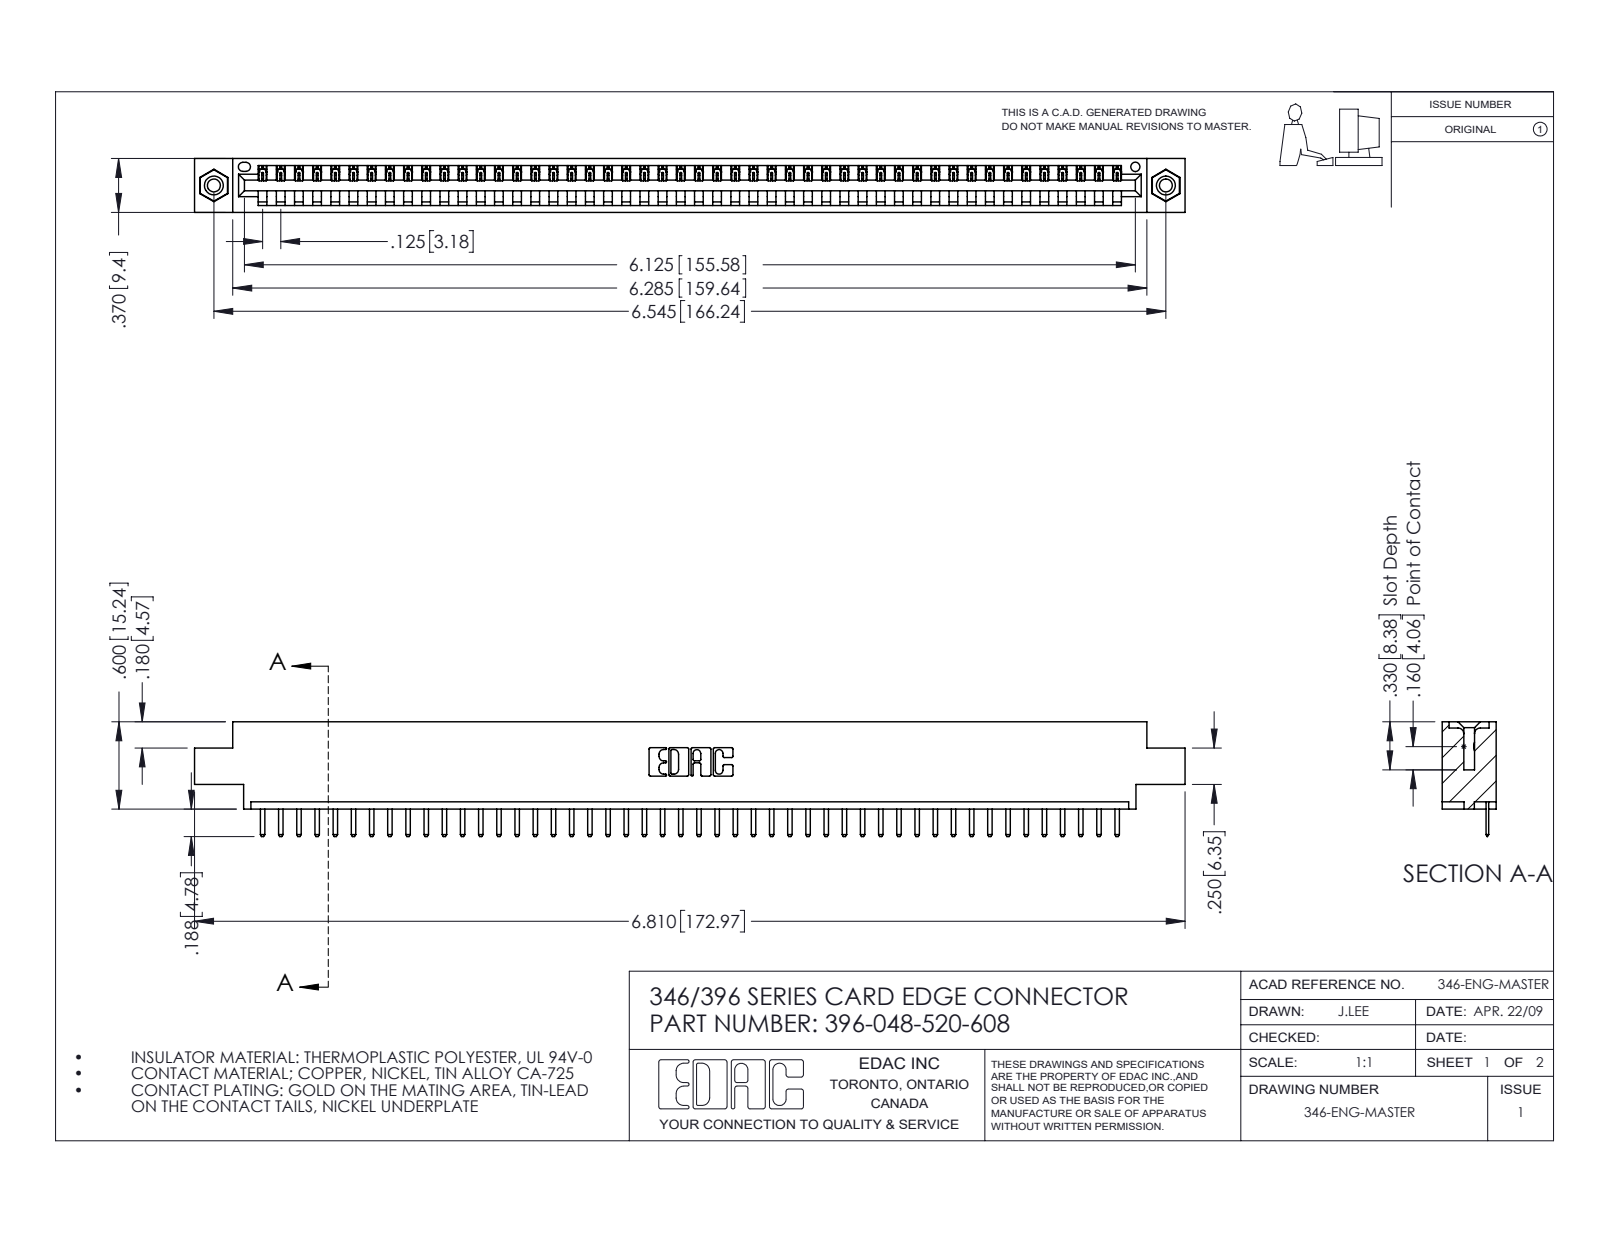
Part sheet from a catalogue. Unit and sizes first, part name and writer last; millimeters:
Units: millimetres
Overall size (bounding box): 173 × 20 × 9.4
Round holes (diameter × count): ⌀2.3 ×2, ⌀3.2 ×2, ⌀4 ×2, ⌀1.6 ×1
Round bosses / shafts (diameter × count): ⌀3.9 ×2
Partial cylindrical surfaces — rounded edges, fillets, slot ends (radius × count): R0.3 ×98, R0.2 ×96, R0.3 ×22, R0.2 ×6, R0.8 ×6, R0.7 ×3, R0.8 ×2, R1 ×2
Main face-to-face distances: 1.2, 8.2, 9.4, 6.4, 5.6, 3.8, 2.5, 4.4, 1.8, 7.6
Hole centre spacings: 6.2, 160.9, 166.2
Volume: 16 300 mm³ · Surface area: 20 160 mm²
Bodies: 51 solids, 3162 faces (2128 planar, 1018 cylindrical, 16 other)
Part name (STEP PRODUCT): 346 Part_0.170 Offset - 0.156 Dia-TI; 345-250-001_345-250-003-102; 345-292-001_345-293-120; 396-048-520-608
STEP written by: SolidWorks 2016 (CONFIG_CONTROL_DESIGN)
